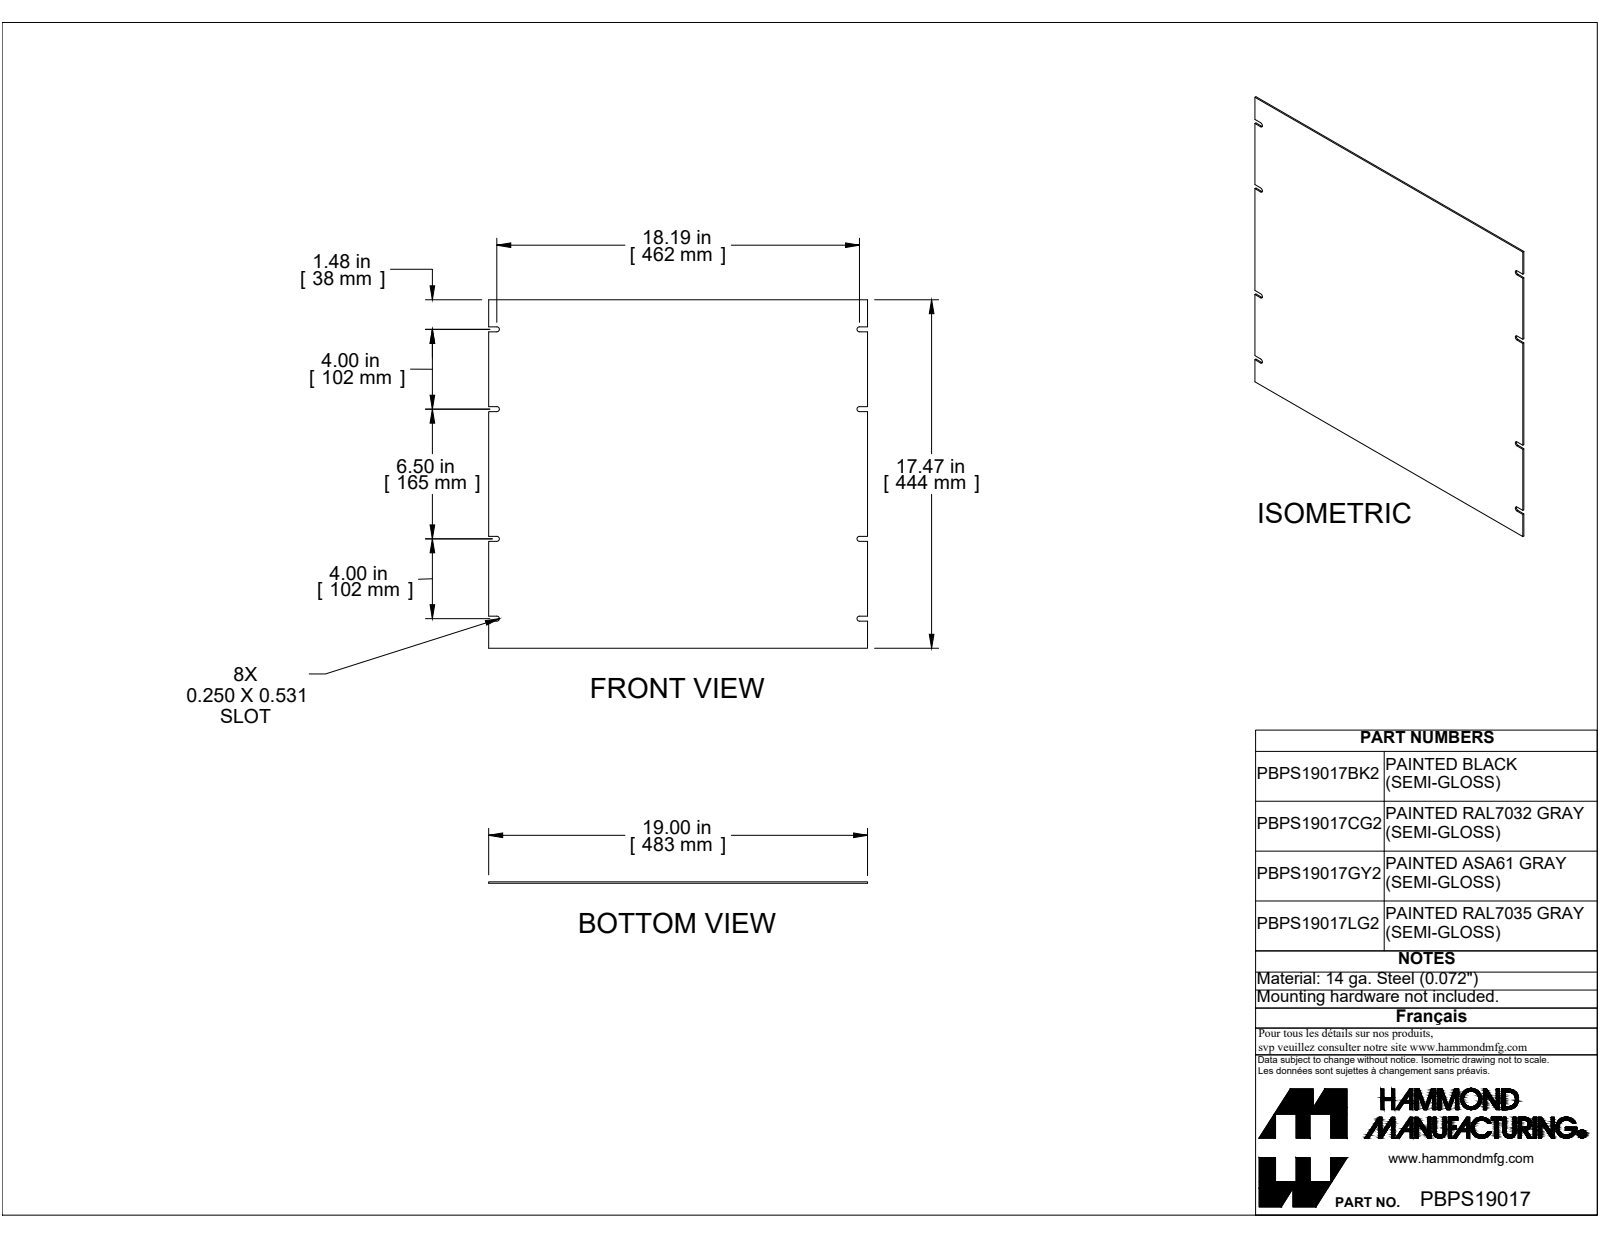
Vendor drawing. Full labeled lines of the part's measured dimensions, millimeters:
Part name (STEP PRODUCT): PBPS19017GY2
STEP written by: SolidWorks 2019 (CONFIG_CONTROL_DESIGN)
Units: millimetres
Bodies: 1 solid, 38 faces (30 planar, 8 cylindrical, 0 other)
Overall size (bounding box): 482.6 × 443.7 × 1.8
Volume: 390 300 mm³ · Surface area: 430 700 mm²
Partial cylindrical surfaces — rounded edges, fillets, slot ends (radius × count): R3.2 ×8
Main face-to-face distances: 1.8, 443.7, 482.6, 6.4, 101.6, 266.7, 142.5, 301.2, 34.5, 40.9
